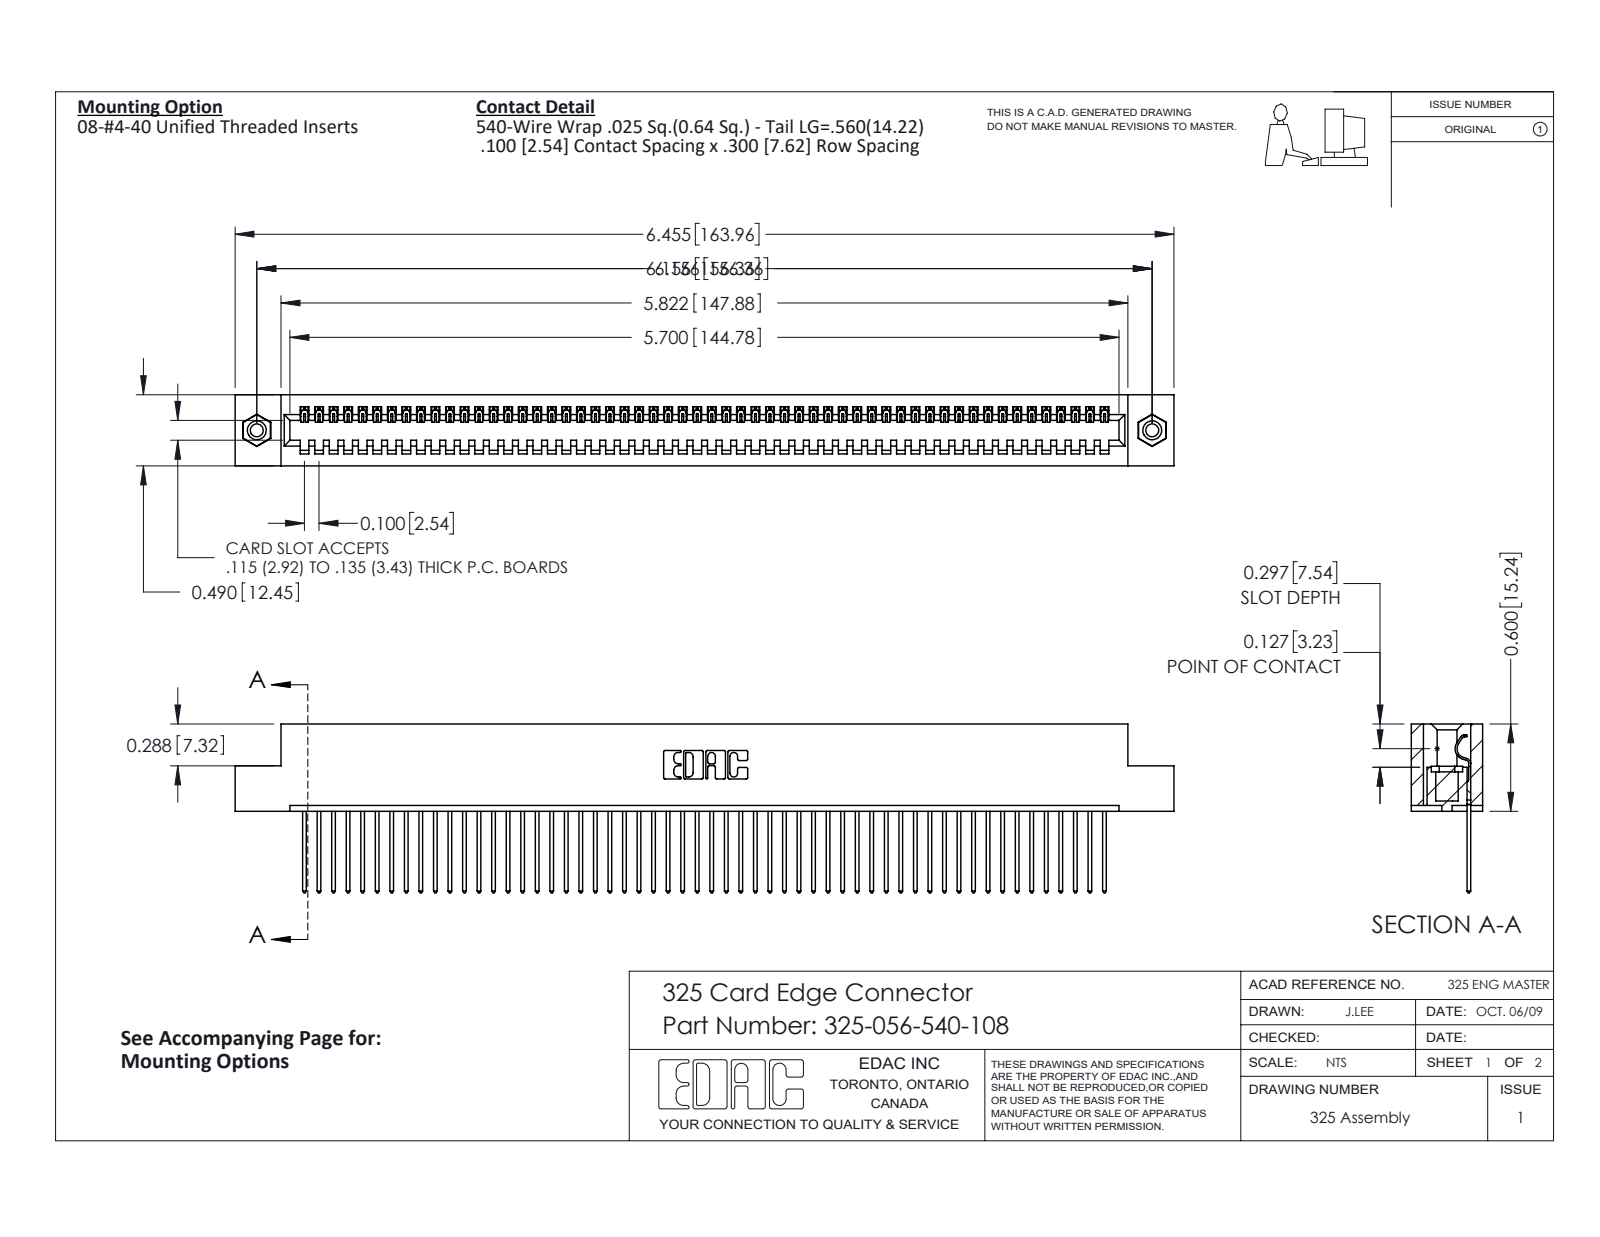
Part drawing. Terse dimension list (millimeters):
name: 325-056-540-108; 325-292-001_325-293-140; 325 Part_TI; 345-250-001_345-250-003-102
written by: SolidWorks 2016 (CONFIG_CONTROL_DESIGN)
unit: mm
bodies: 59 solids, 3422 faces (2454 planar, 952 cylindrical, 16 other)
size: 164 × 29.5 × 12.4
volume: 20 990 mm³; area: 23 750 mm²
holes: 2× ⌀2.3, 2× ⌀3.2, 2× ⌀4.1
bosses: 2× ⌀3.9
rounds: 112× R0.2, 112× R0.3, 22× R0.3, 6× R0.2, 6× R0.8, 3× R0.7, 1× R0.4, 1× R0.6
face distances: 2.1, 10.3, 12.4, 2.7, 9.7, 0.6, 7.6, 8.3, 14.2, 6.7
hole spacings: 156.4
